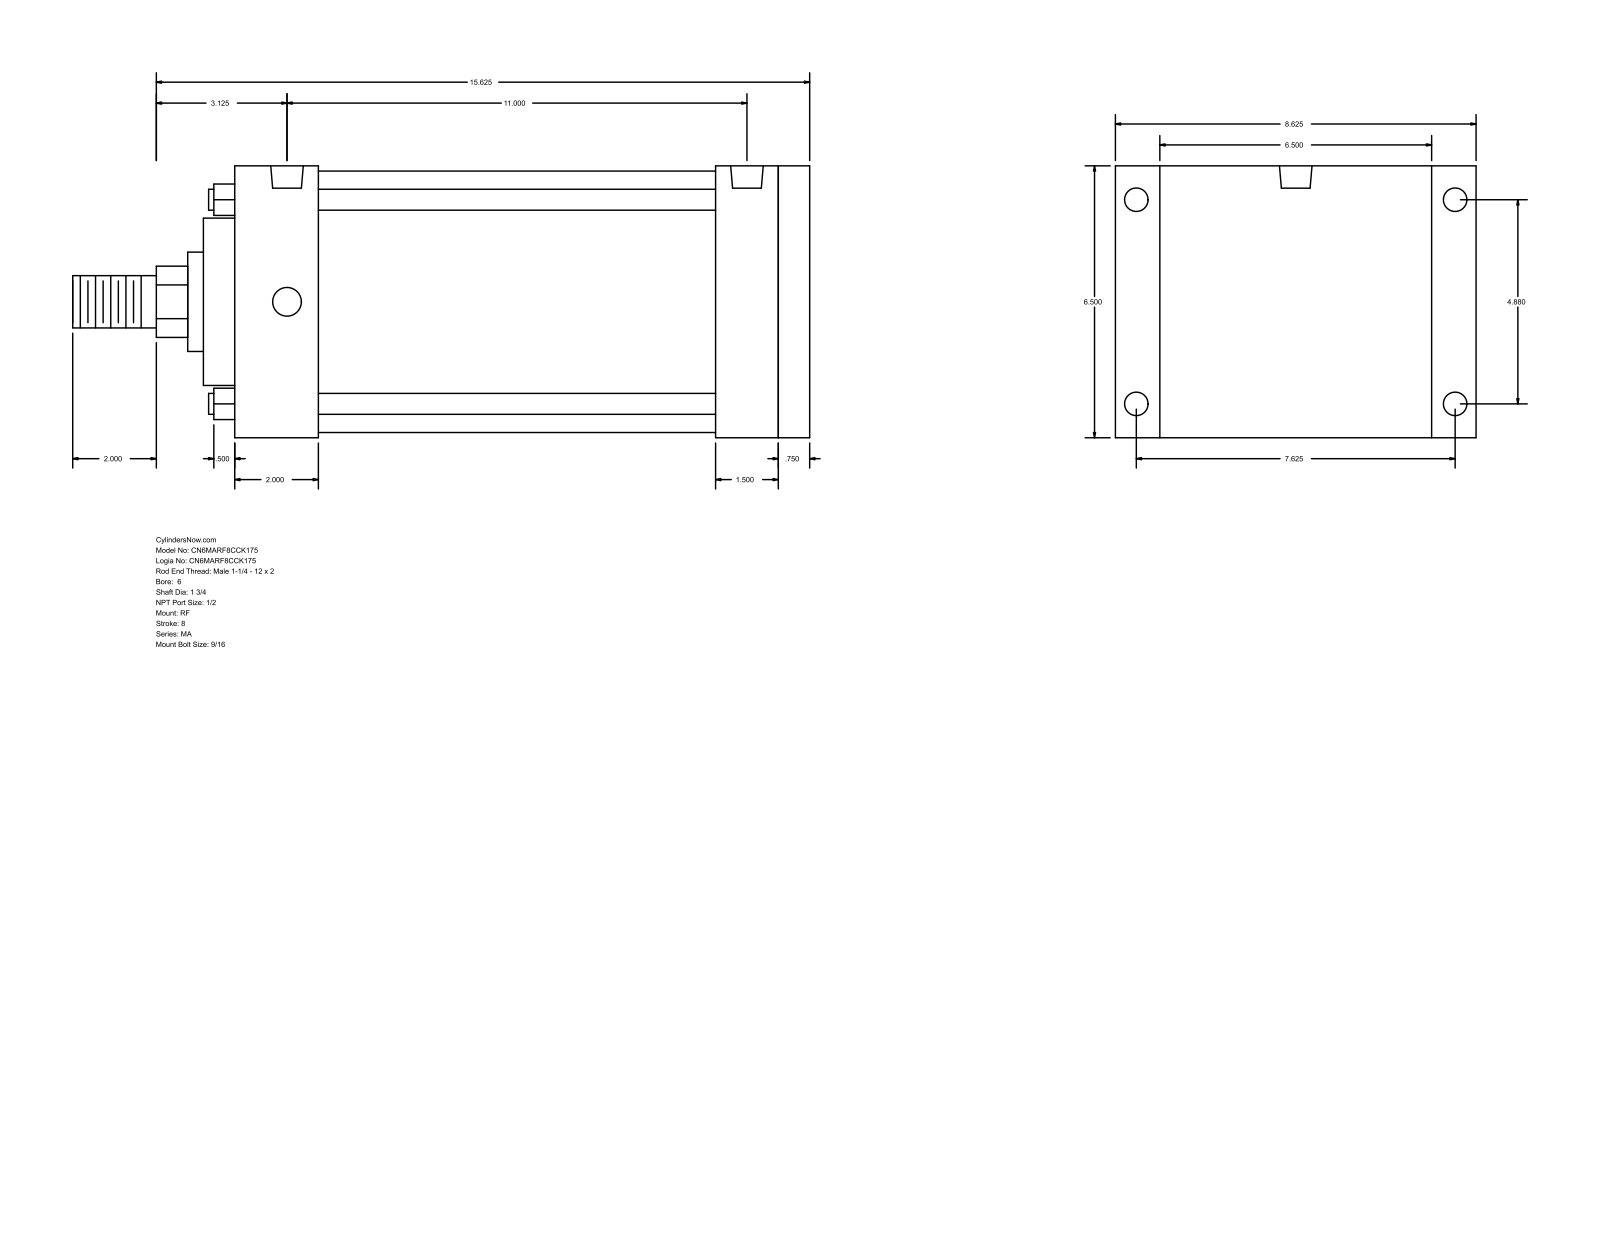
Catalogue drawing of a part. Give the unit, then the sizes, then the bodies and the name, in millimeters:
Units: millimetres
Overall size (bounding box): 447.68 × 219.07 × 165.1
Round holes (diameter × count): ⌀14.29 ×4, ⌀17.46 ×4, ⌀19.77 ×2
Round bosses / shafts (diameter × count): ⌀12.7 ×4, ⌀158.75 ×1, ⌀101.6 ×1, ⌀60.33 ×1, ⌀44.45 ×1, ⌀31.75 ×1
Partial cylindrical surfaces — rounded edges, fillets, slot ends (radius × count): R21.63 ×1
Main face-to-face distances: 165.1, 349.26, 330.2, 19.06, 50.8, 19.05, 279.4, 298.46, 292.11, 241.31
Hole centre spacings: 123.96, 193.68, 229.95, 279.39
Bodies: 0 solids, 94 faces (65 planar, 29 cylindrical, 0 other)
Part name (STEP PRODUCT): MA_RF__0600_1.75
STEP written by: GSSL Pune (CONFIG_CONTROL_DESIGN)
